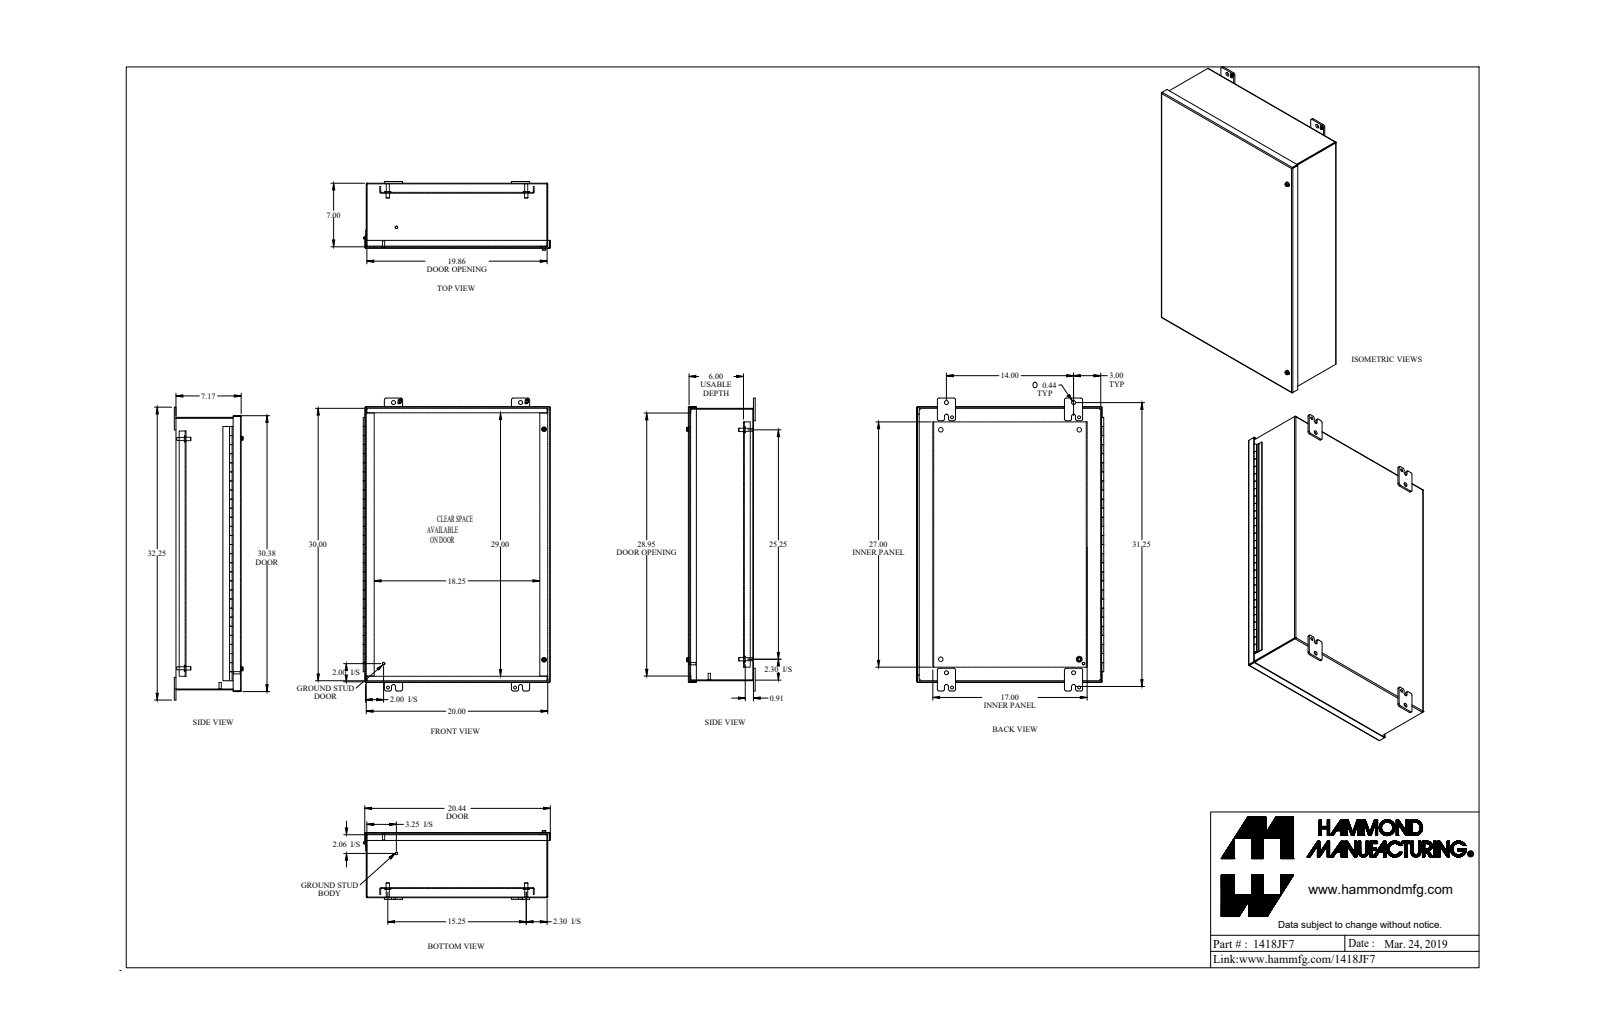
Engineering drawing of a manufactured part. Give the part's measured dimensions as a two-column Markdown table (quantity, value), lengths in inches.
| quantity | value |
| --- | --- |
| part name | 1418JF7_Default |
| STEP written by | SolidWorks 2018 (CONFIG_CONTROL_DESIGN) |
| units | inches |
| bodies | 32 solids, 996 faces (617 planar, 337 cylindrical, 42 other) |
| overall size | 32.25 × 20.604 × 7.571 |
| volume | 228.9 in³ |
| surface area | 5 639 in² |
| round holes (diameter × count) | 0.313 × 6, 0.437 × 4, 0.5 × 4, 0.26 × 2, 0.266 × 2, 0.28 × 2, 0.29 × 2, 0.307 × 2, 0.397 × 2, 0.445 × 2, 0.187 × 1, 3.5 × 1 |
| round bosses / shafts (diameter × count) | 0.65 × 4, 0.375 × 4, 0.33 × 4, 1 × 2, 0.51 × 2, 0.5 × 2, 0.39 × 2, 0.281 × 2 |
| partial cylindrical surfaces (radius × count) | 0.188 × 24, 0.25 × 20, 0.036 × 12, 0.108 × 12, 0.218 × 8, 0.133 × 6, 0.06 × 5, 0.125 × 4 |
| main face-to-face distances | 0.072, 7.1, 7.172, 7.028, 0.095, 5.996, 6.091, 1.104, 1.032, 6.068 |
| hole center spacings | 14.749, 29.498, 1.736, 14, 15.25, 29.75, 32.88, 1.907 |
